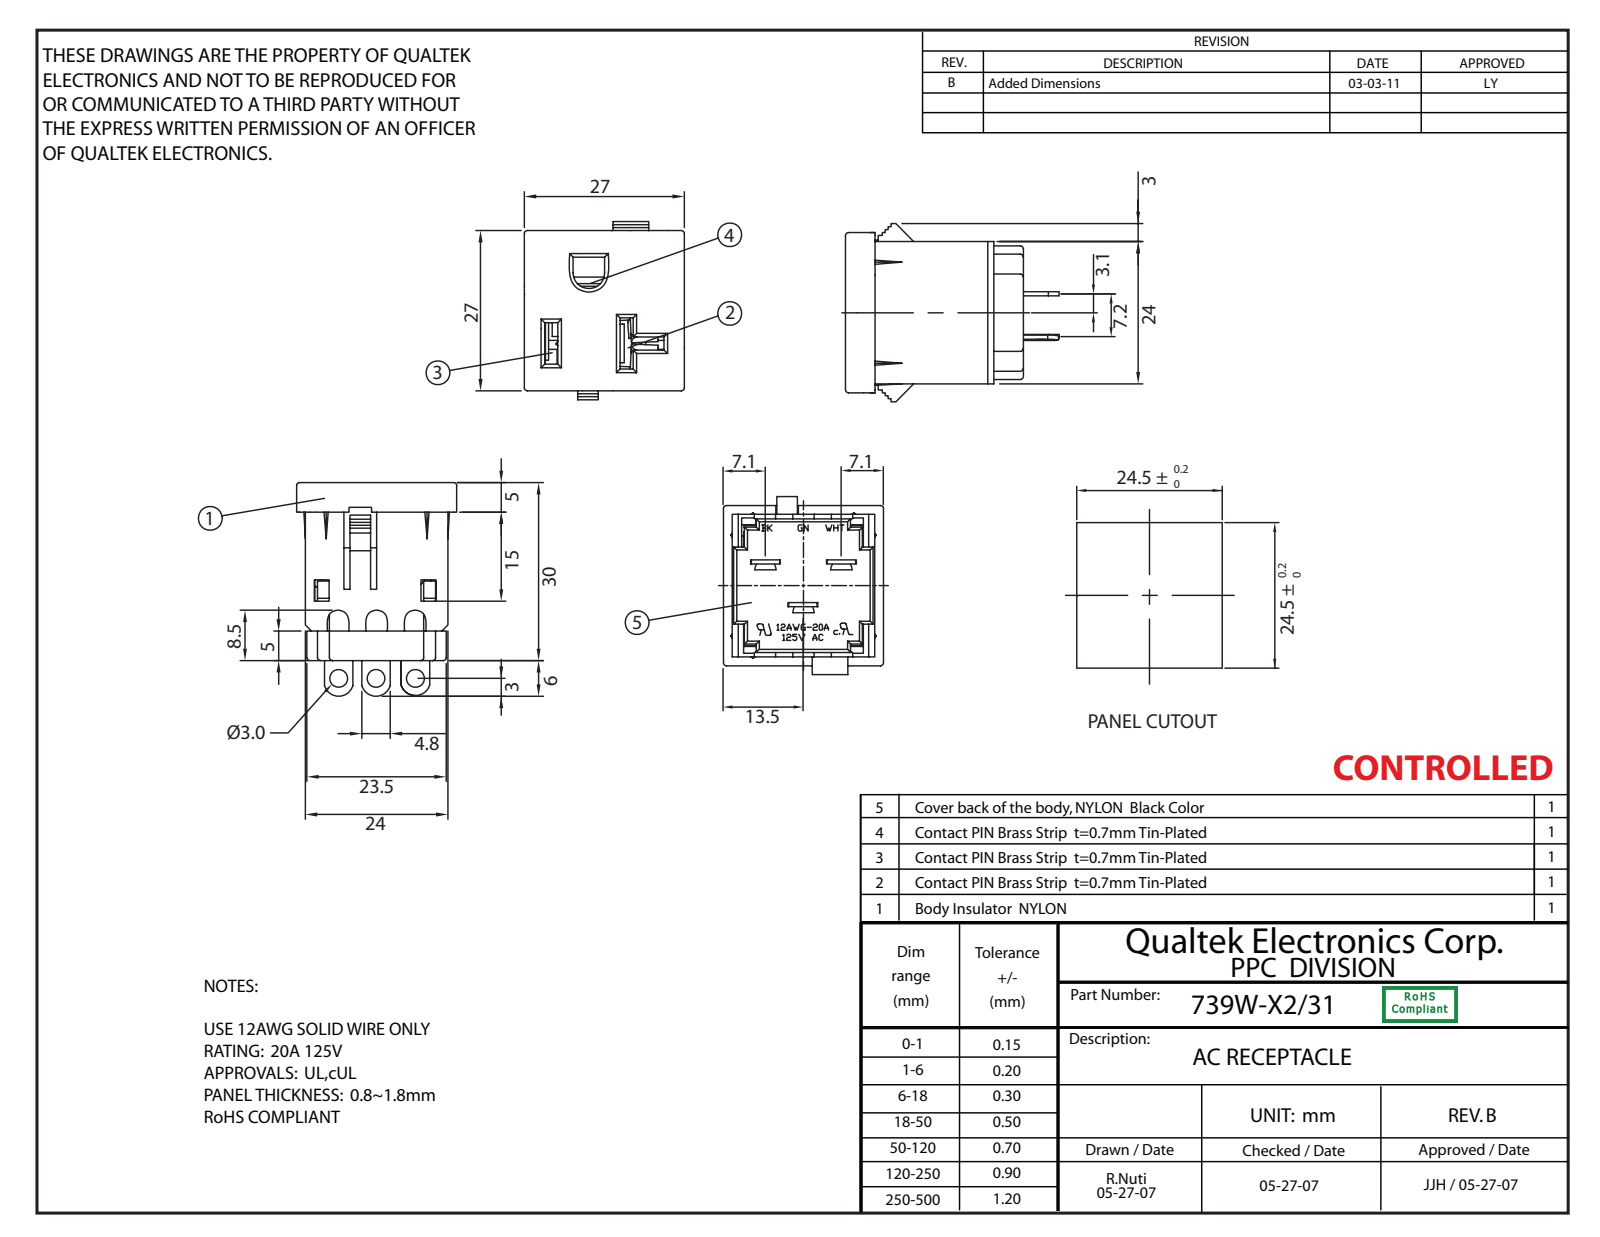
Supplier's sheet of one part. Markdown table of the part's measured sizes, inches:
| quantity | value |
| --- | --- |
| part name | RF6005-002; RF6003A; RF6005-001; RF6005-003 (+1 more) |
| STEP written by | SolidWorks 2016 (AUTOMOTIVE_DESIGN) |
| units | inches |
| bodies | 6 solids, 681 faces (521 planar, 134 cylindrical, 26 other) |
| overall size | 1.417 × 1.161 × 1.063 |
| volume | 0.584 in³ |
| surface area | 19.19 in² |
| round holes (diameter × count) | 0.039 × 4, 0.118 × 3 |
| partial cylindrical surfaces (radius × count) | 0.02 × 34, 0.008 × 12, 0.039 × 9, 0.071 × 8, 0.047 × 6, 0.091 × 4, 0.094 × 3, 0.118 × 3 |
| main face-to-face distances | 0.059, 0.079, 0.945, 0.039, 0.138, 0.028, 0.866, 1.004, 0.118, 0.433 |
| hole center spacings | 0.048, 0.114, 0.15, 0.252, 0.316, 0.354, 0.465, 0.642 |
